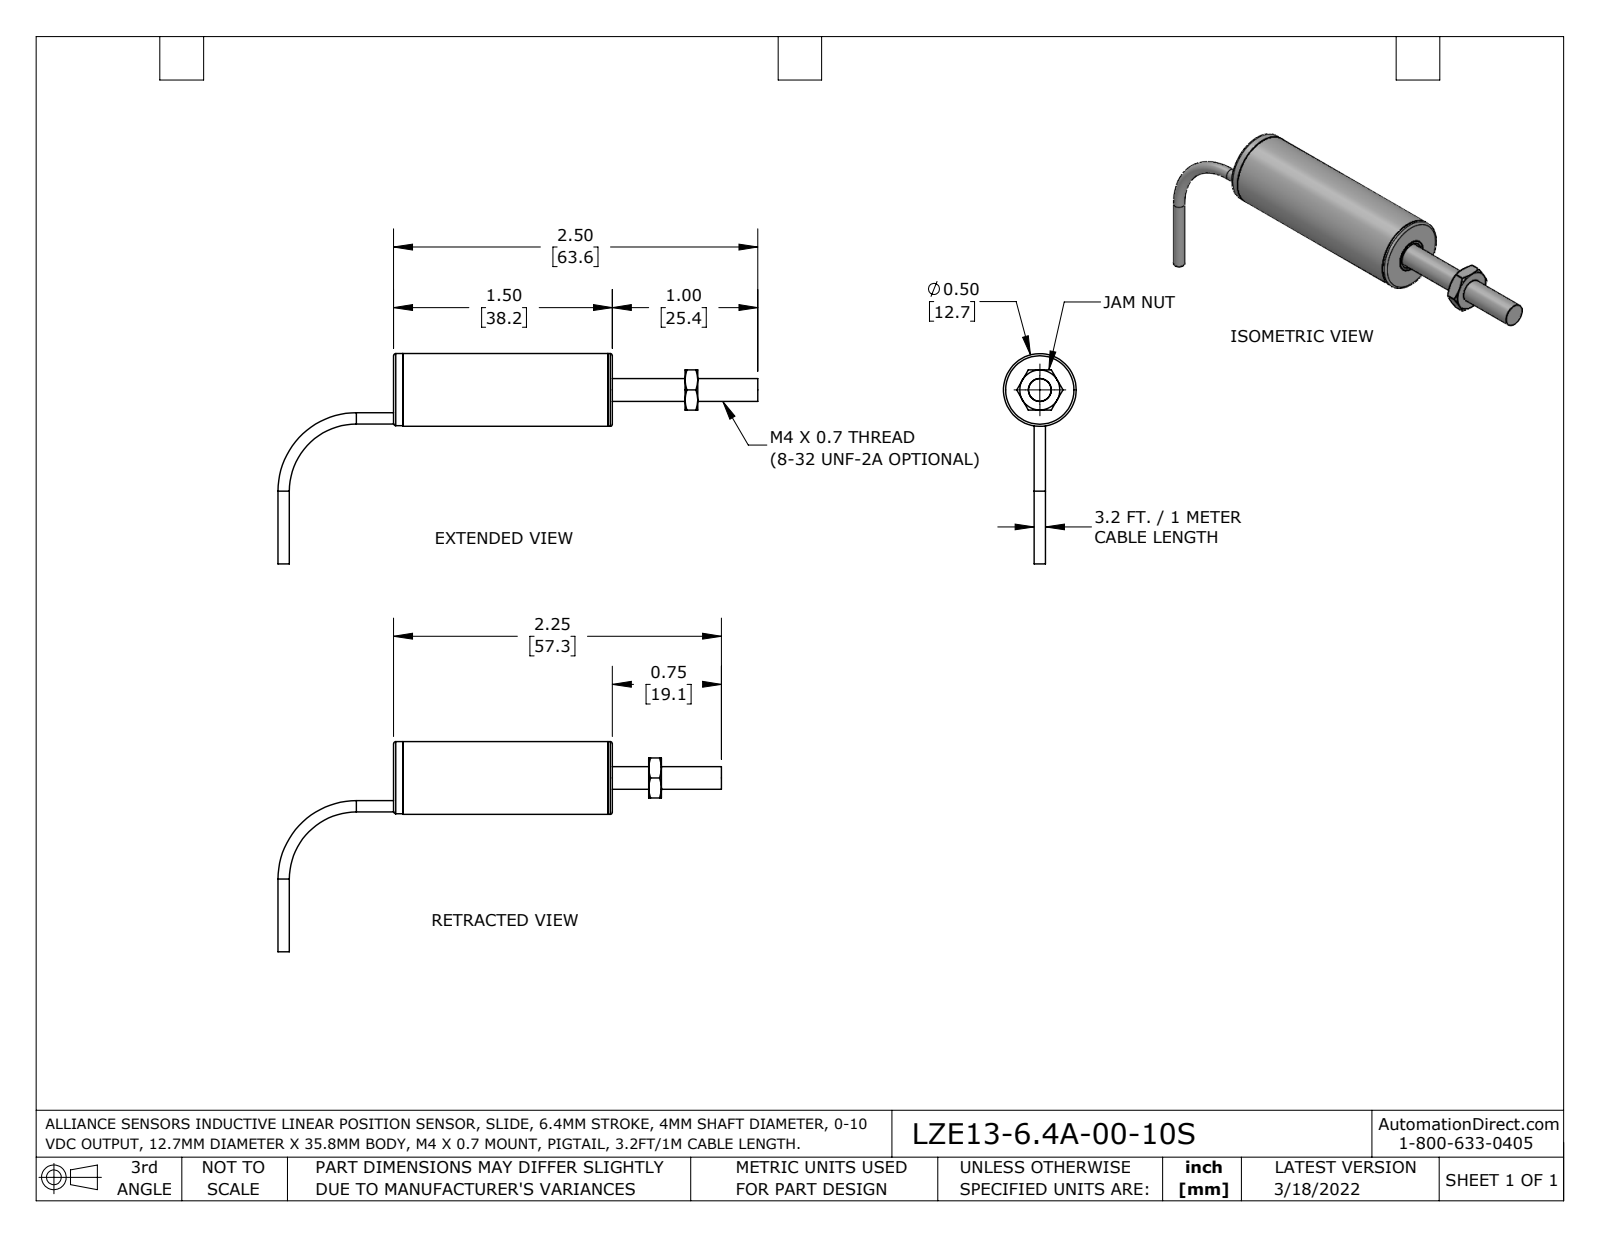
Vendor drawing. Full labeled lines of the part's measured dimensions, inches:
Part name (STEP PRODUCT): 3300-0020-XX_3300-0020-.25; LZE13-6.4A-00-10S; 3120-0034-XX-Z_3120-0034-.25-Z; 3120-0033-XX_3120-0033-.25 (+6 more)
STEP written by: SolidWorks 2021 (AUTOMOTIVE_DESIGN)
Units: inches
Bodies: 9 solids, 98 faces (32 planar, 38 cylindrical, 28 other)
Overall size (bounding box): 3.299 × 1.445 × 0.5
Volume: 0.151 in³ · Surface area: 9.928 in²
Round holes (diameter × count): ⌀0.078 ×1, ⌀0.157 ×1, ⌀0.187 ×1, ⌀0.223 ×1
Round bosses / shafts (diameter × count): ⌀0.5 ×1, ⌀0.468 ×1, ⌀0.222 ×1, ⌀0.156 ×1, ⌀0.1 ×1, ⌀0.078 ×1
Partial cylindrical surfaces — rounded edges, fillets, slot ends (radius × count): R0.047 ×1
Main face-to-face distances: 0.079, 0.062, 0.276, 0.094, 1.504, 1.442, 1.41, 1.348, 0.031, 0.5
Hole centre spacings: 0.195
